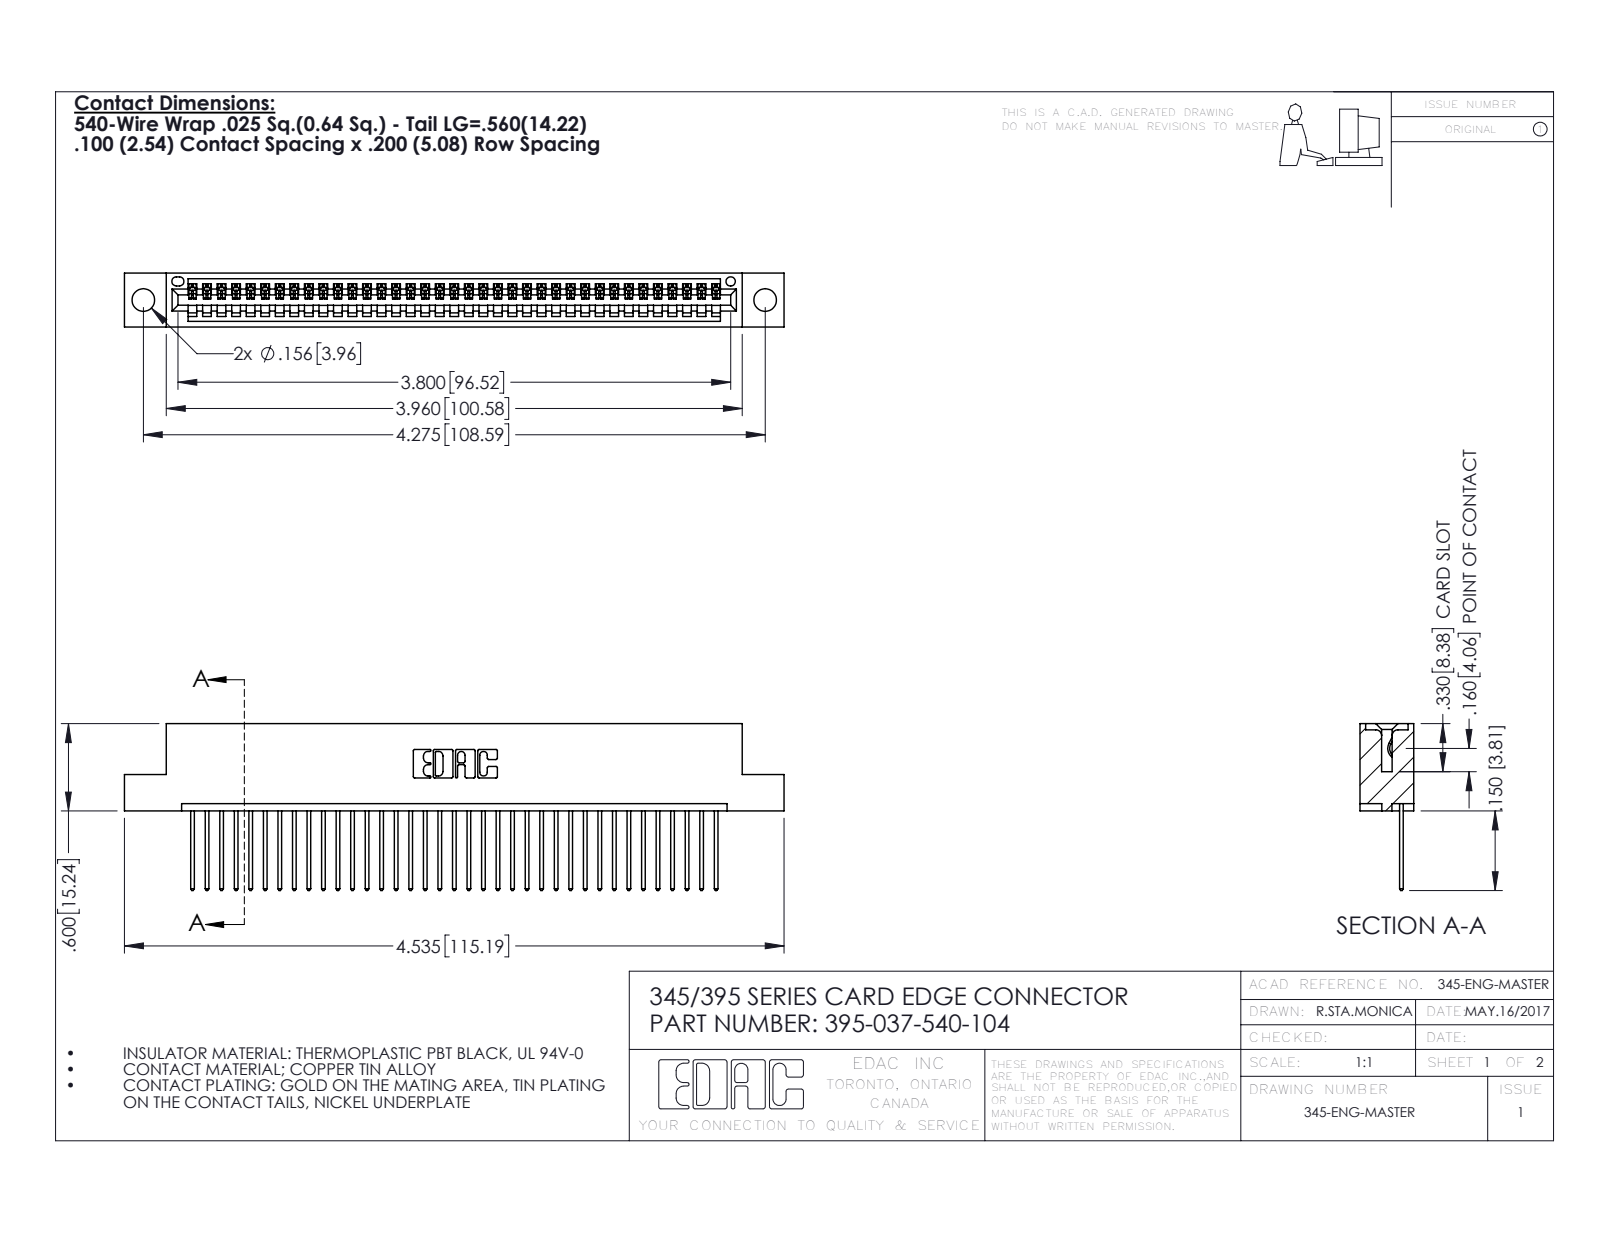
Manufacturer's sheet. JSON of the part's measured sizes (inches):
{"part_name": "395-037-540-104; 345-292-001_345-293-140; 345 Part_Flush Mounting Lugs - 0.156 Dia-TH", "step_written_by": "SolidWorks 2016 (CONFIG_CONTROL_DESIGN)", "units": "inches", "bodies": {"solids": 38, "faces": 2272, "planar": 1560, "cylindrical": 712, "other": 0}, "overall_size": [4.535, 1.147, 0.37], "volume_in3": 0.663, "surface_area_in2": 22.53, "round_holes": [[0.156, 2], [0.064, 1]], "partial_cylinders_radius": [[0.006, 74], [0.01, 74], [0.01, 22], [0.007, 6], [0.031, 6], [0.026, 3], [0.031, 2], [0.04, 2]], "face_to_face_distances": [0.298, 0.072, 0.2, 0.37, 0.098, 0.272, 0.025, 0.225, 0.149, 0.072], "hole_center_spacings": [0.27, 4.039, 4.275]}
